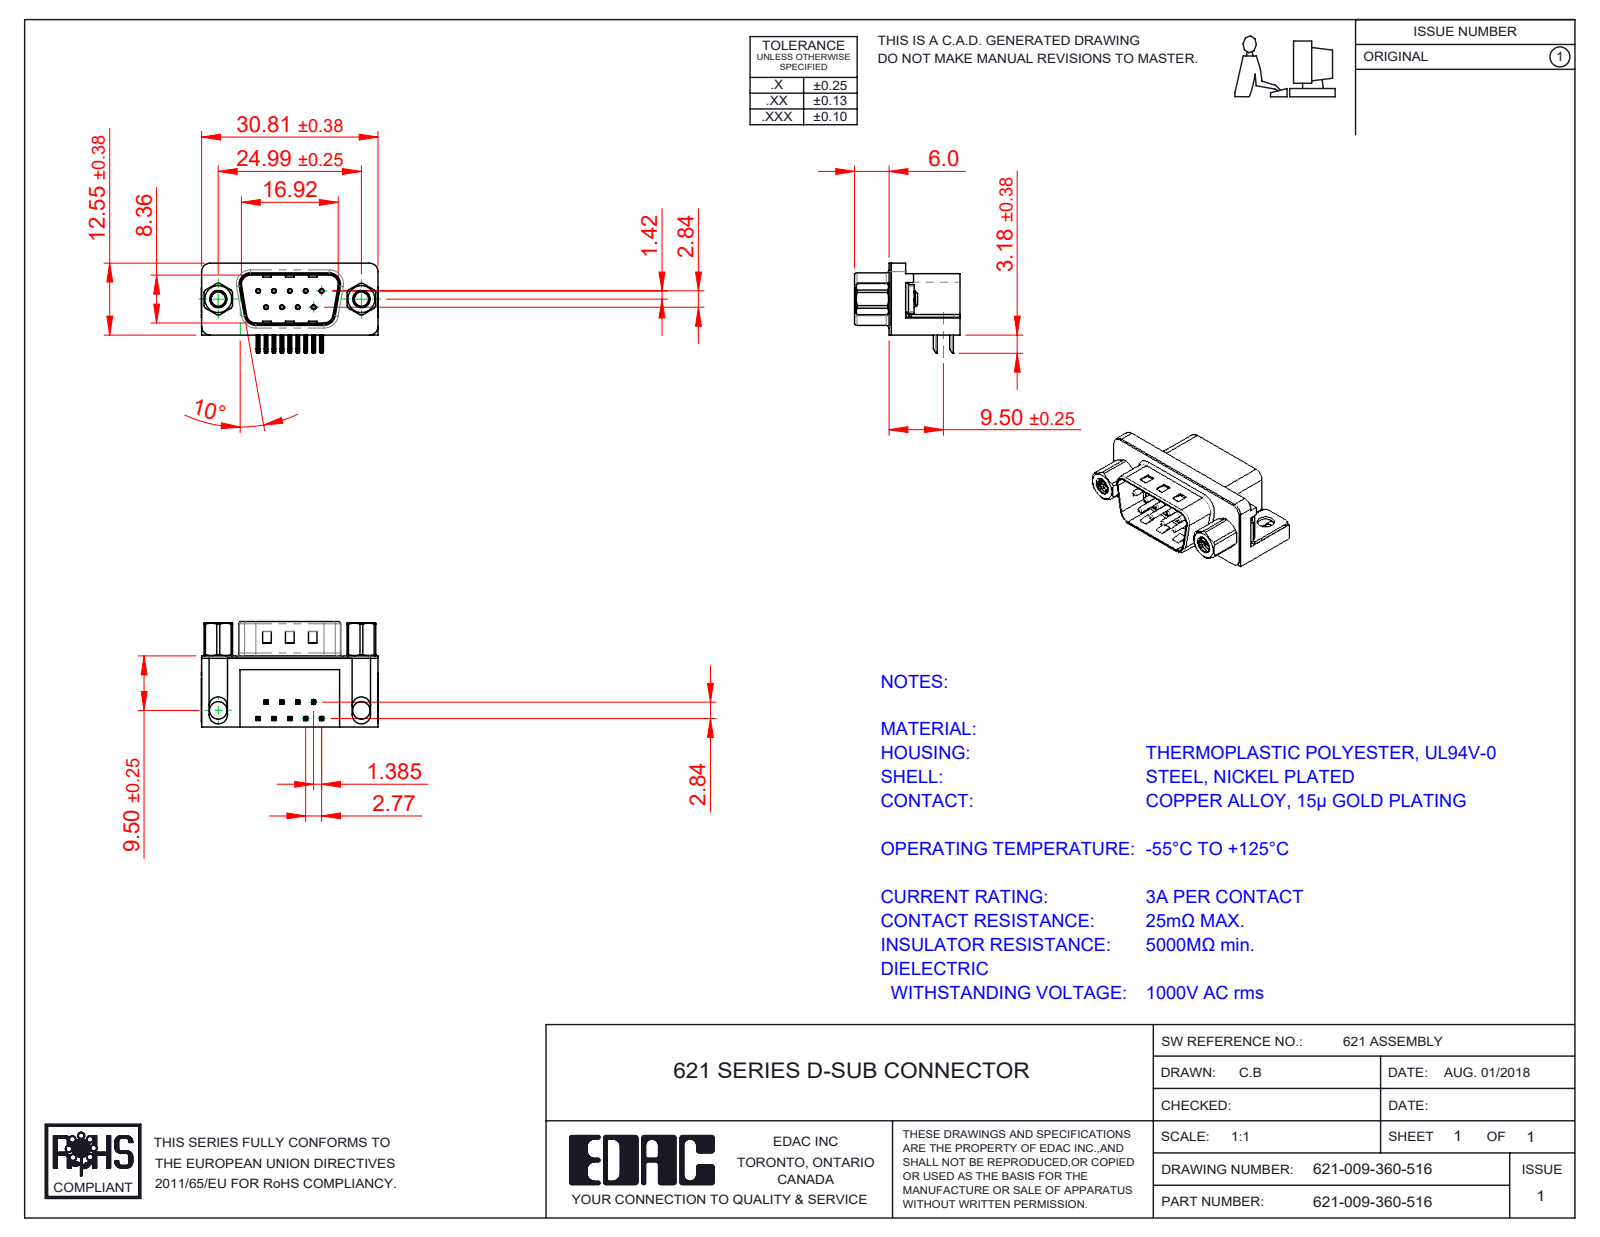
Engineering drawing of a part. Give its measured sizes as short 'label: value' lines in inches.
name: 621 M3 Threaded Rivet; 621 Contact Bottom; 621-009-360-516; 621 Thru Hole Board Mount (+4 more)
written by: SolidWorks 2016 (CONFIG_CONTROL_DESIGN)
unit: in
bodies: 17 solids, 1137 faces (593 planar, 411 cylindrical, 133 other)
size: 1.216 × 0.724 × 0.619
volume: 0.213 in³; area: 7.657 in²
holes: 9× ⌀0.014, 9× ⌀0.031, 2× ⌀0.098, 2× ⌀0.12, 2× ⌀0.157, 2× ⌀0.189, 2× ⌀0.197
bosses: 9× ⌀0.03, 2× ⌀0.193, 2× ⌀0.187, 2× ⌀0.154, 2× ⌀0.118
rounds: 44× R0.01, 18× R0.005, 16× R0.039, 9× R0.02, 8× R0.059, 8× R0.063, 4× R0.035, 4× R0.079
face distances: 0.016, 0.472, 0.488, 0.407, 0.02, 0.374, 0.098, 0.114, 0.083, 0.014
hole spacings: 0.124, 0.109, 0.218, 0.198, 0.198, 0.327, 0.294, 0.295
